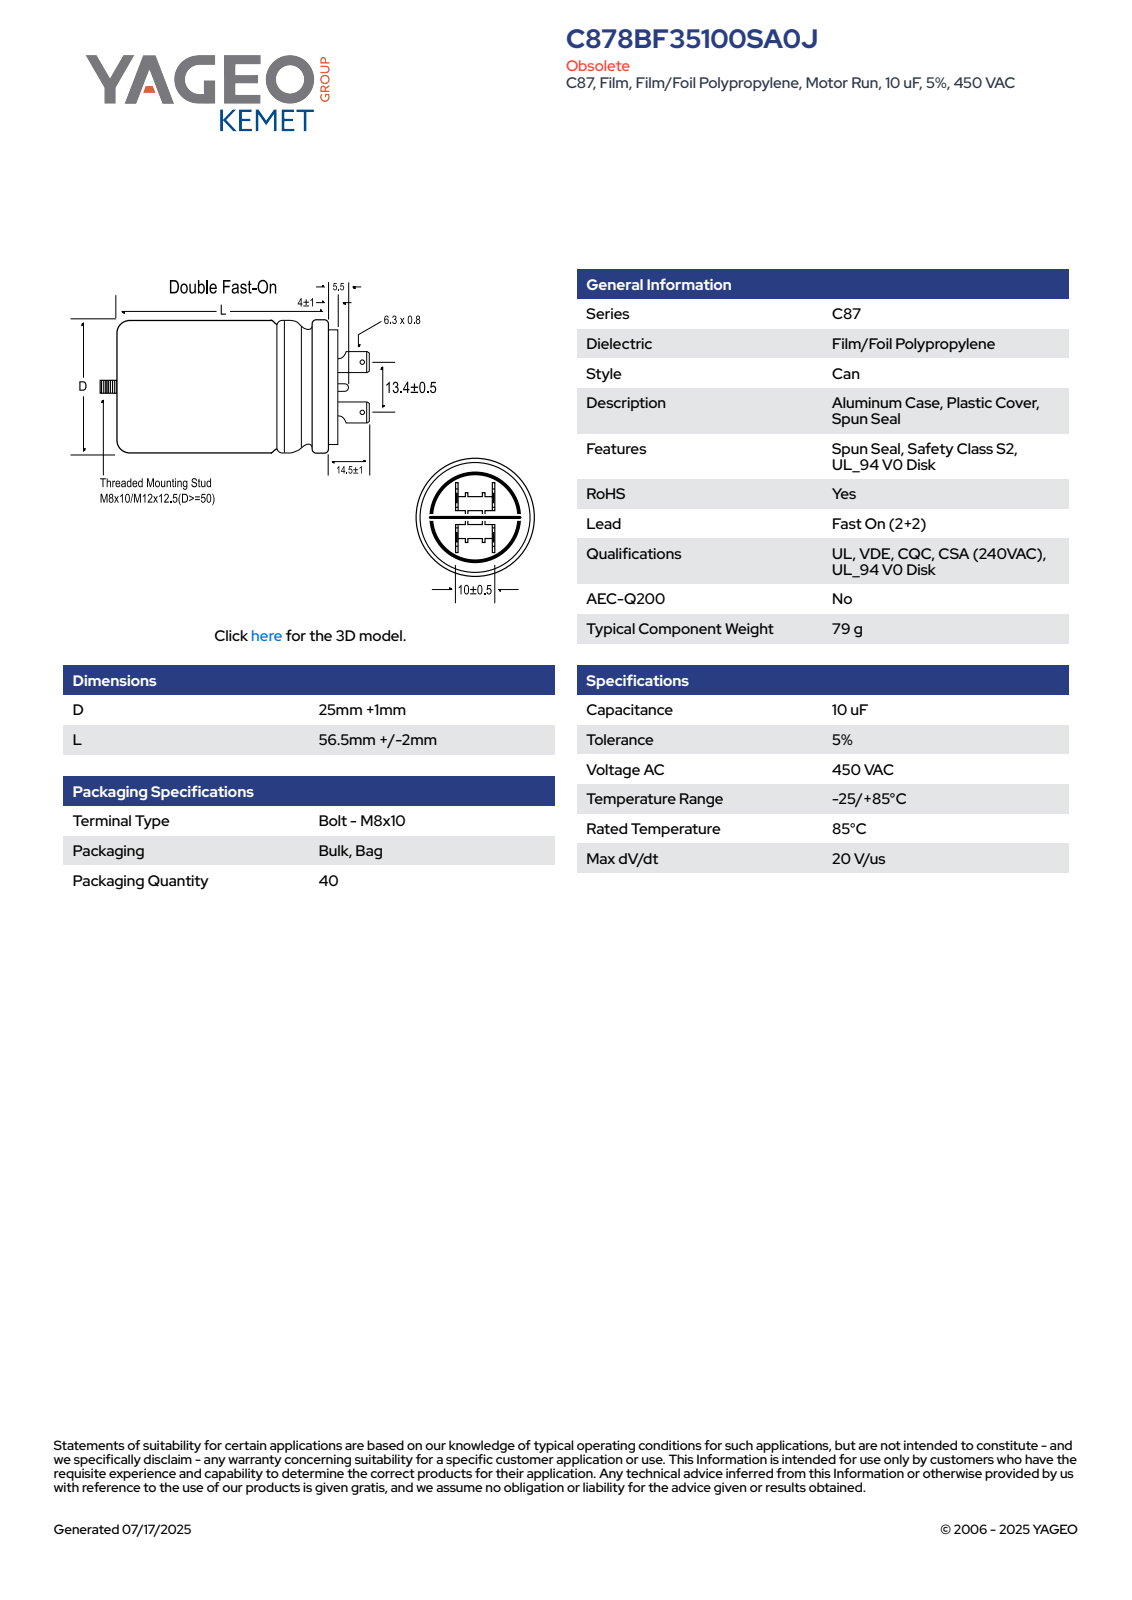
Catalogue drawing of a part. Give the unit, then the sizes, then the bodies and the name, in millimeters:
Units: millimetres
Overall size (bounding box): 105.5 × 36 × 36
Round holes (diameter × count): ⌀1.2 ×2
Round bosses / shafts (diameter × count): ⌀36 ×1, ⌀30.73 ×1, ⌀8 ×1
Partial cylindrical surfaces — rounded edges, fillets, slot ends (radius × count): R0.25 ×9, R4 ×2, R17.99 ×1
Main face-to-face distances: 85, 0.8, 9.7, 74.15, 10.85, 10.5, 8.9, 80, 5.85, 5
Hole centre spacings: 13.9
Volume: 83 392 mm³ · Surface area: 12 478 mm²
Bodies: 1 solid, 156 faces (55 planar, 58 cylindrical, 43 other)
Part name (STEP PRODUCT): CFM_C87DF_35X78_D36L80
STEP written by: SolidWorks 2014 (AUTOMOTIVE_DESIGN)
